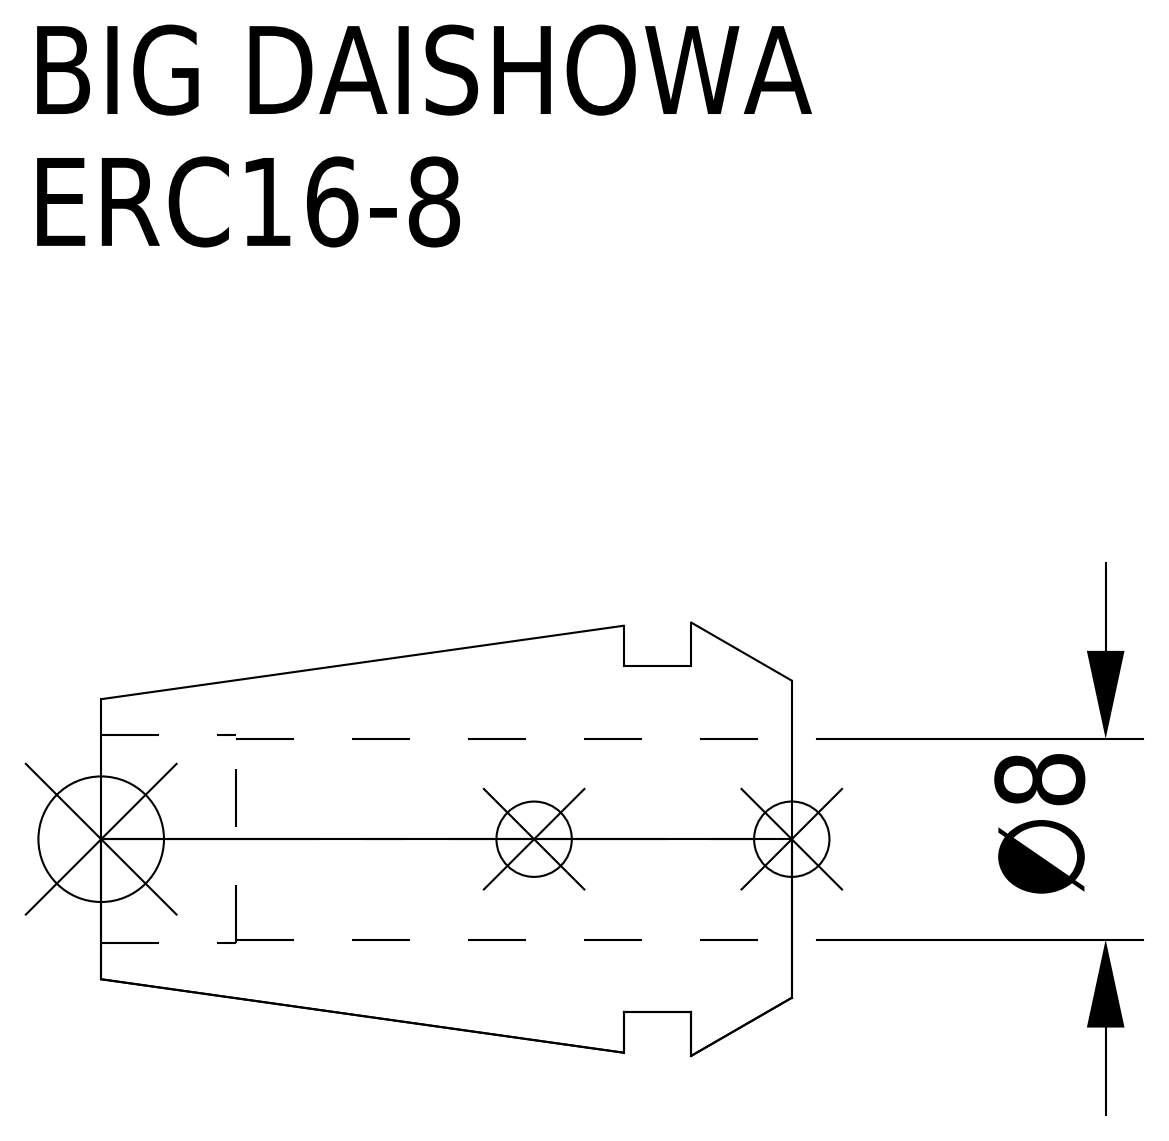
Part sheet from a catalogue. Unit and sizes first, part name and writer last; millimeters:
Units: millimetres
Overall size (bounding box): 27.5 × 17.25 × 17.25
Round holes (diameter × count): ⌀8 ×1, ⌀8.3 ×1
Round bosses / shafts (diameter × count): ⌀13.8 ×1
Main face-to-face distances: 2.7, 4, 6.7, 27.5, 23.5, 20.8, 22.14, 18.14, 15.44, 5.36
Volume: 2 992 mm³ · Surface area: 2 243 mm²
Bodies: 1 solid, 15 faces (5 planar, 6 cylindrical, 4 other)
Part name (STEP PRODUCT): ERC16-8
STEP written by: CREO PARAMETRIC BY PTC INC, 2016380 (AUTOMOTIVE_DESIGN)
